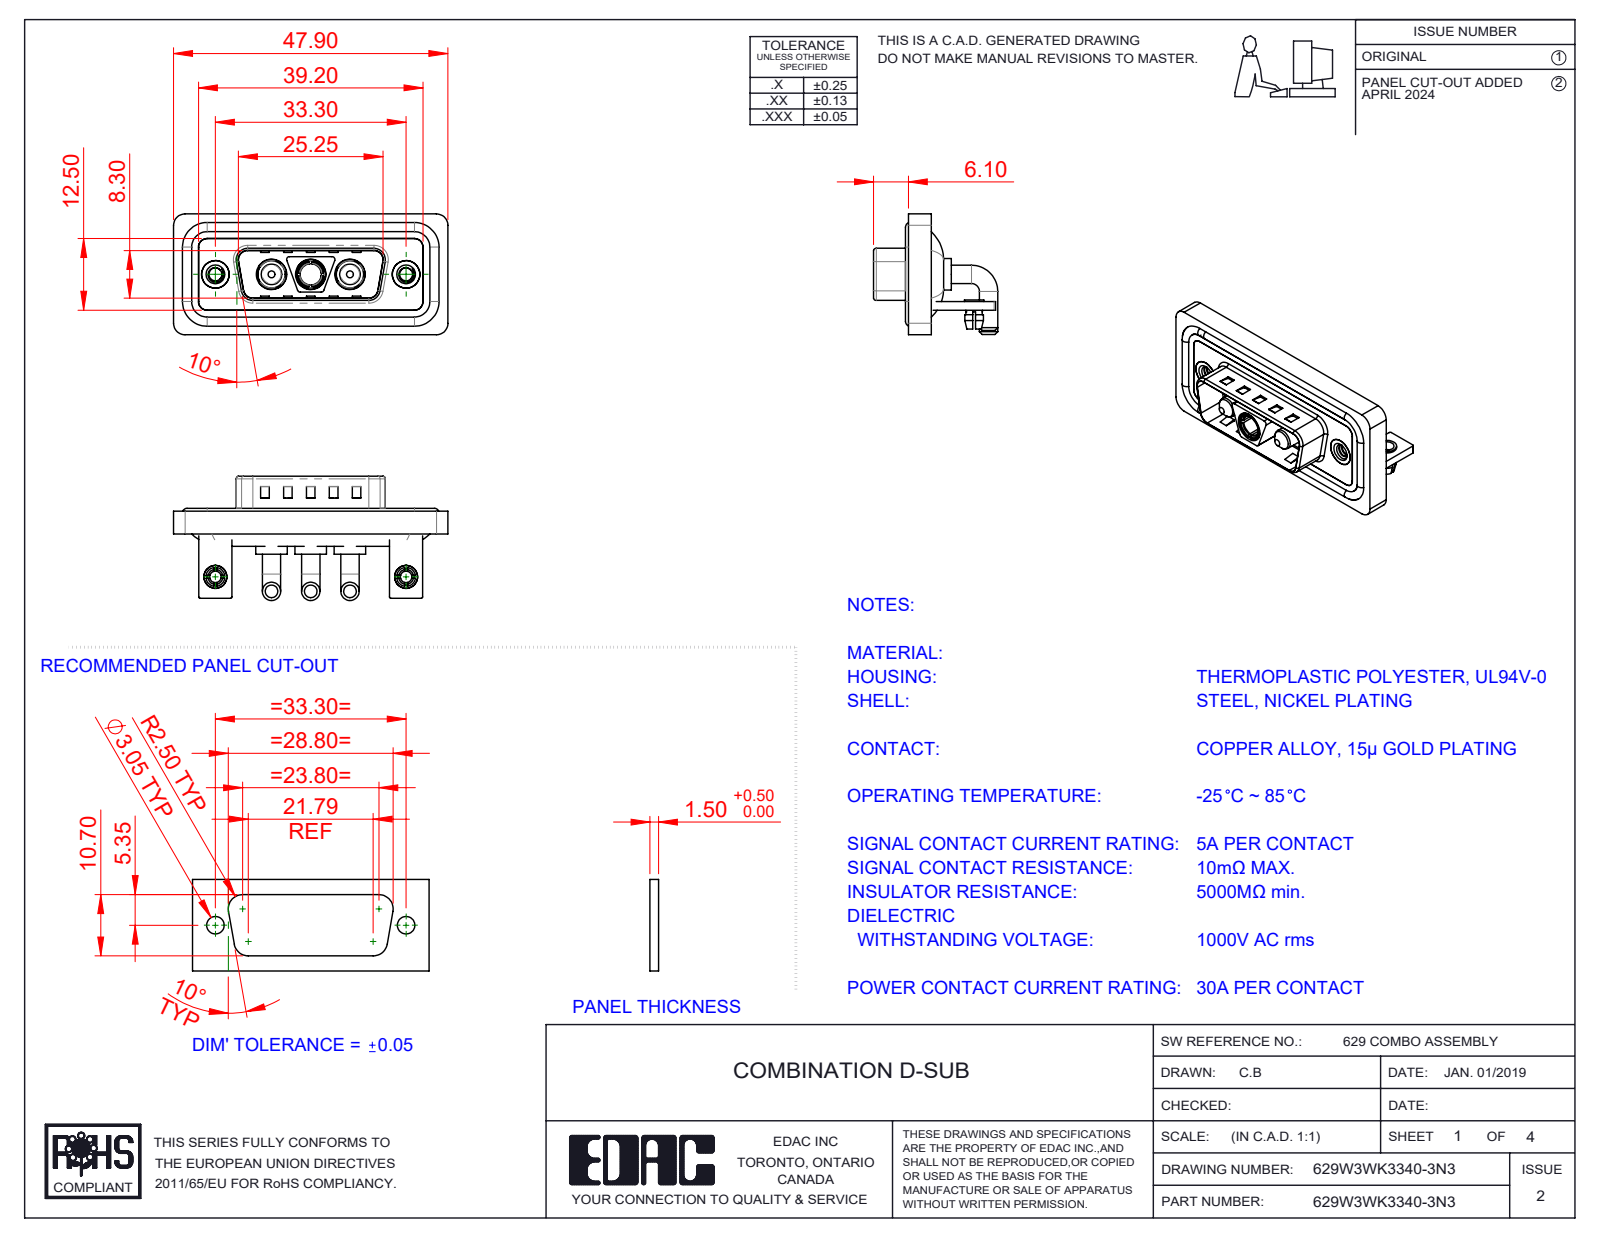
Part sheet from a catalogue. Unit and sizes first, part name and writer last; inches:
Units: inches
Overall size (bounding box): 1.886 × 0.854 × 0.831
Round holes (diameter × count): ⌀0.191 ×3, ⌀0.209 ×3, ⌀0.079 ×2, ⌀0.089 ×2, ⌀0.098 ×2, ⌀0.126 ×2, ⌀0.157 ×2, ⌀0.189 ×2, ⌀0.197 ×2, ⌀0.146 ×1
Round bosses / shafts (diameter × count): ⌀0.126 ×6, ⌀0.063 ×4, ⌀0.217 ×3, ⌀0.205 ×3, ⌀0.187 ×3, ⌀0.148 ×3, ⌀0.193 ×2, ⌀0.157 ×2
Partial cylindrical surfaces — rounded edges, fillets, slot ends (radius × count): R0.079 ×21, R0.059 ×18, R0.01 ×16, R0.02 ×13, R0.063 ×8, R0.024 ×4, R0.026 ×4, R0.035 ×4
Main face-to-face distances: 0.016, 0.059, 0.031, 0.114, 0.043, 0.083, 0.146, 0.063, 0.047, 0.177
Hole centre spacings: 0.27, 0.386, 0.656, 0.925, 1.311, 0.539
Volume: 0.383 in³ · Surface area: 15.92 in²
Bodies: 17 solids, 753 faces (299 planar, 306 cylindrical, 148 other)
Part name (STEP PRODUCT): 629Combo Threaded Rivet_3; 629Combo Stabilizer Bracket; 629Combo Board Lock; 629Combo Shell Rear_15 Contacts (+6 more)
STEP written by: SolidWorks 2023 (CONFIG_CONTROL_DESIGN)
